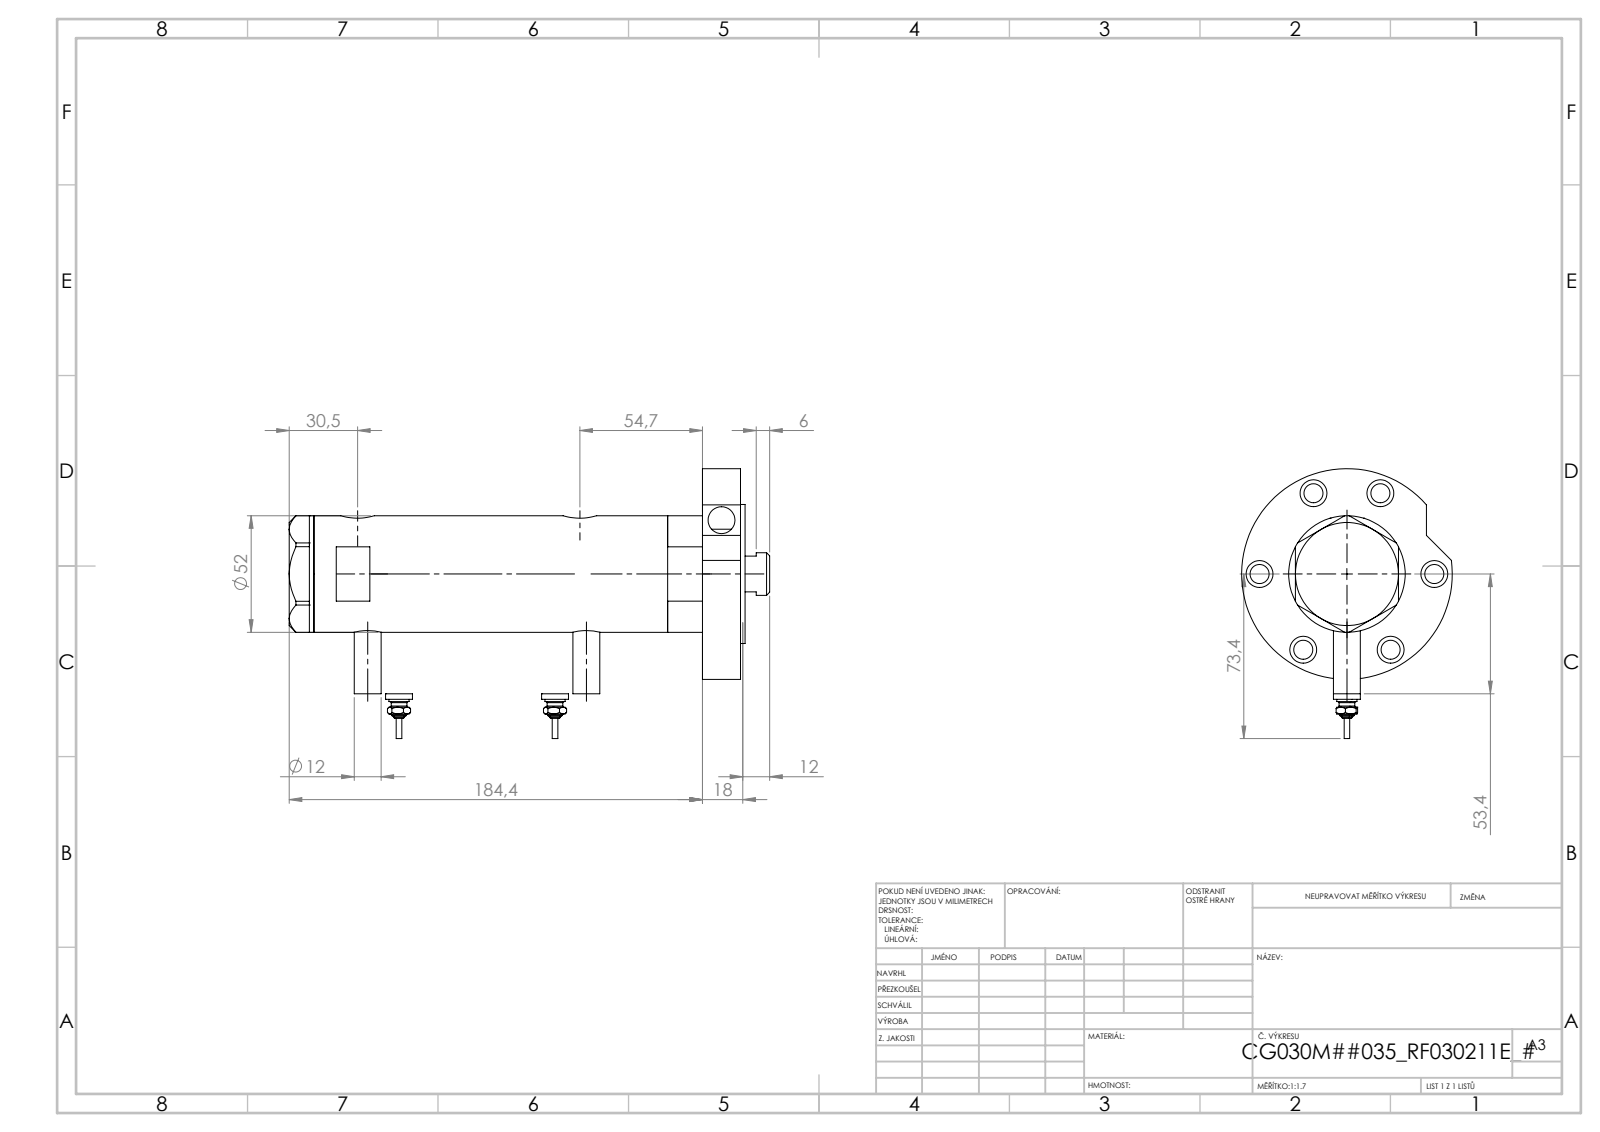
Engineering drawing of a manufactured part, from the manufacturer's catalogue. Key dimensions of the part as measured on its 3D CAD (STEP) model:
Part name (STEP PRODUCT): V270CG_SWITCH; V270CG_VC; V270CG_MIDDLE; V270CG_FRONT (+2 more)
STEP written by: SolidWorks 2019 (CONFIG_CONTROL_DESIGN)
Units: millimetres
Bodies: 7 solids, 290 faces (106 planar, 110 cylindrical, 74 other)
Overall size (bounding box): 184.02 × 105.3 × 94
Volume: 412 772 mm³ · Surface area: 102 033 mm²
Round holes (diameter × count): ⌀12 ×7, ⌀8.5 ×6, ⌀5 ×2, ⌀9.73 ×2, ⌀12.5 ×2, ⌀15 ×2, ⌀6.5 ×1, ⌀20 ×1, ⌀21.5 ×1, ⌀30 ×1, ⌀33 ×1, ⌀40 ×1
Round bosses / shafts (diameter × count): ⌀12 ×3, ⌀9 ×2, ⌀7 ×2, ⌀4.34 ×2, ⌀2.4 ×2, ⌀94 ×1, ⌀62 ×1, ⌀52 ×1
Main face-to-face distances: 17, 140.46, 157.46, 51.9, 2, 159.46, 19, 23.8, 116.66, 133.66
Hole centre spacings: 39, 2.9, 4.5, 43.34, 61.75, 64.65, 64.85, 66.25
